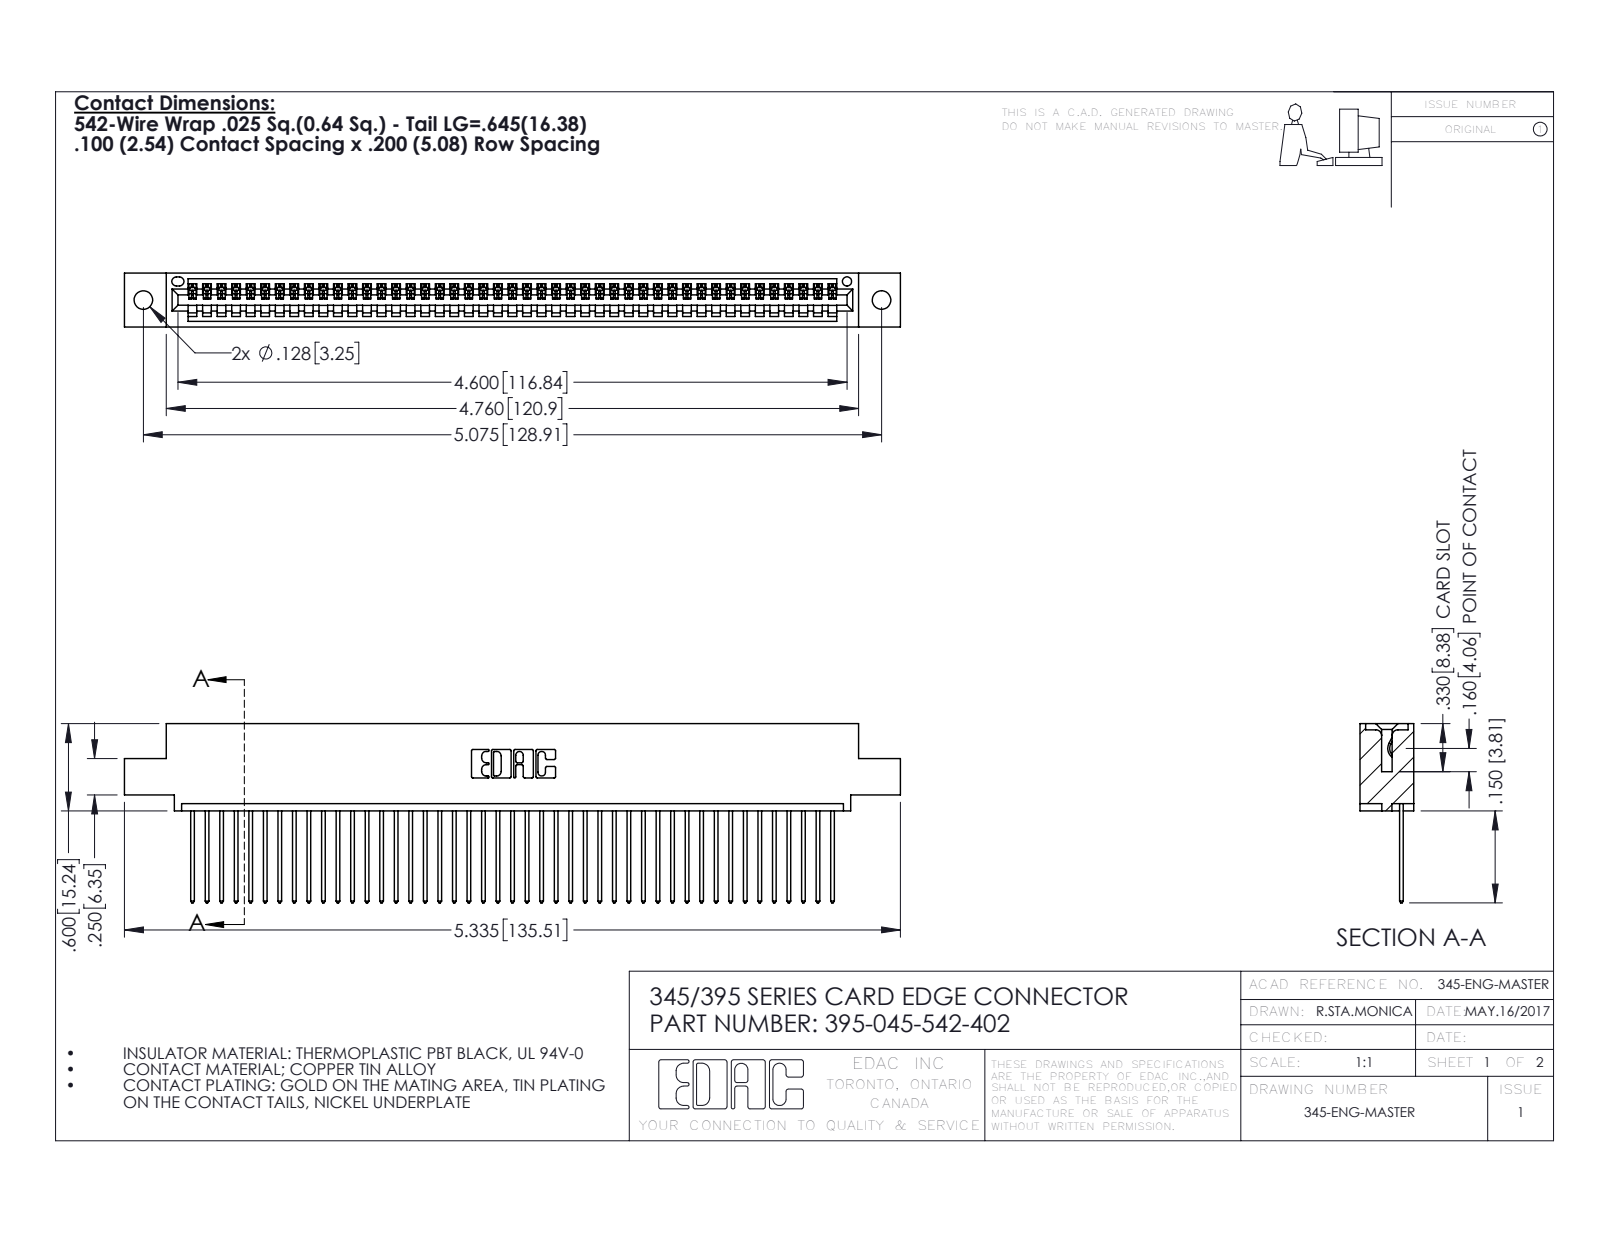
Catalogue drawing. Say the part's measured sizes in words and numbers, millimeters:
The part is named "345-292-001_345-293-142; 345 Part_0.110 Offset - 0.128 Dia; 395-045-542-402". Its 3-D file was written by "SolidWorks 2016 (CONFIG_CONTROL_DESIGN)". It is 46 solids with 2740 faces: 1884 planar, 856 cylindrical and 0 other. Overall it measures 135.5 by 31.3 by 9.4 millimeters. Its volume is 12 900 cubic millimeters and its surface area 17 610 square millimeters. Round holes: 2 of diameter 3.3, 1 of diameter 1.6. Partial cylindrical surfaces (rounded edges, fillets, slot ends): 90 of radius 0.2, 90 of radius 0.3, 22 of radius 0.3, 6 of radius 0.2, 6 of radius 0.8, 3 of radius 0.7, 2 of radius 0.8, 2 of radius 1. The main face-to-face distances are 1.8, 7.6, 9.4, 2.5, 6.9, 0.6, 5.1, 5.7, 3.8, 1.8. The hole center spacings are 6.9, 122.9, 128.9.
